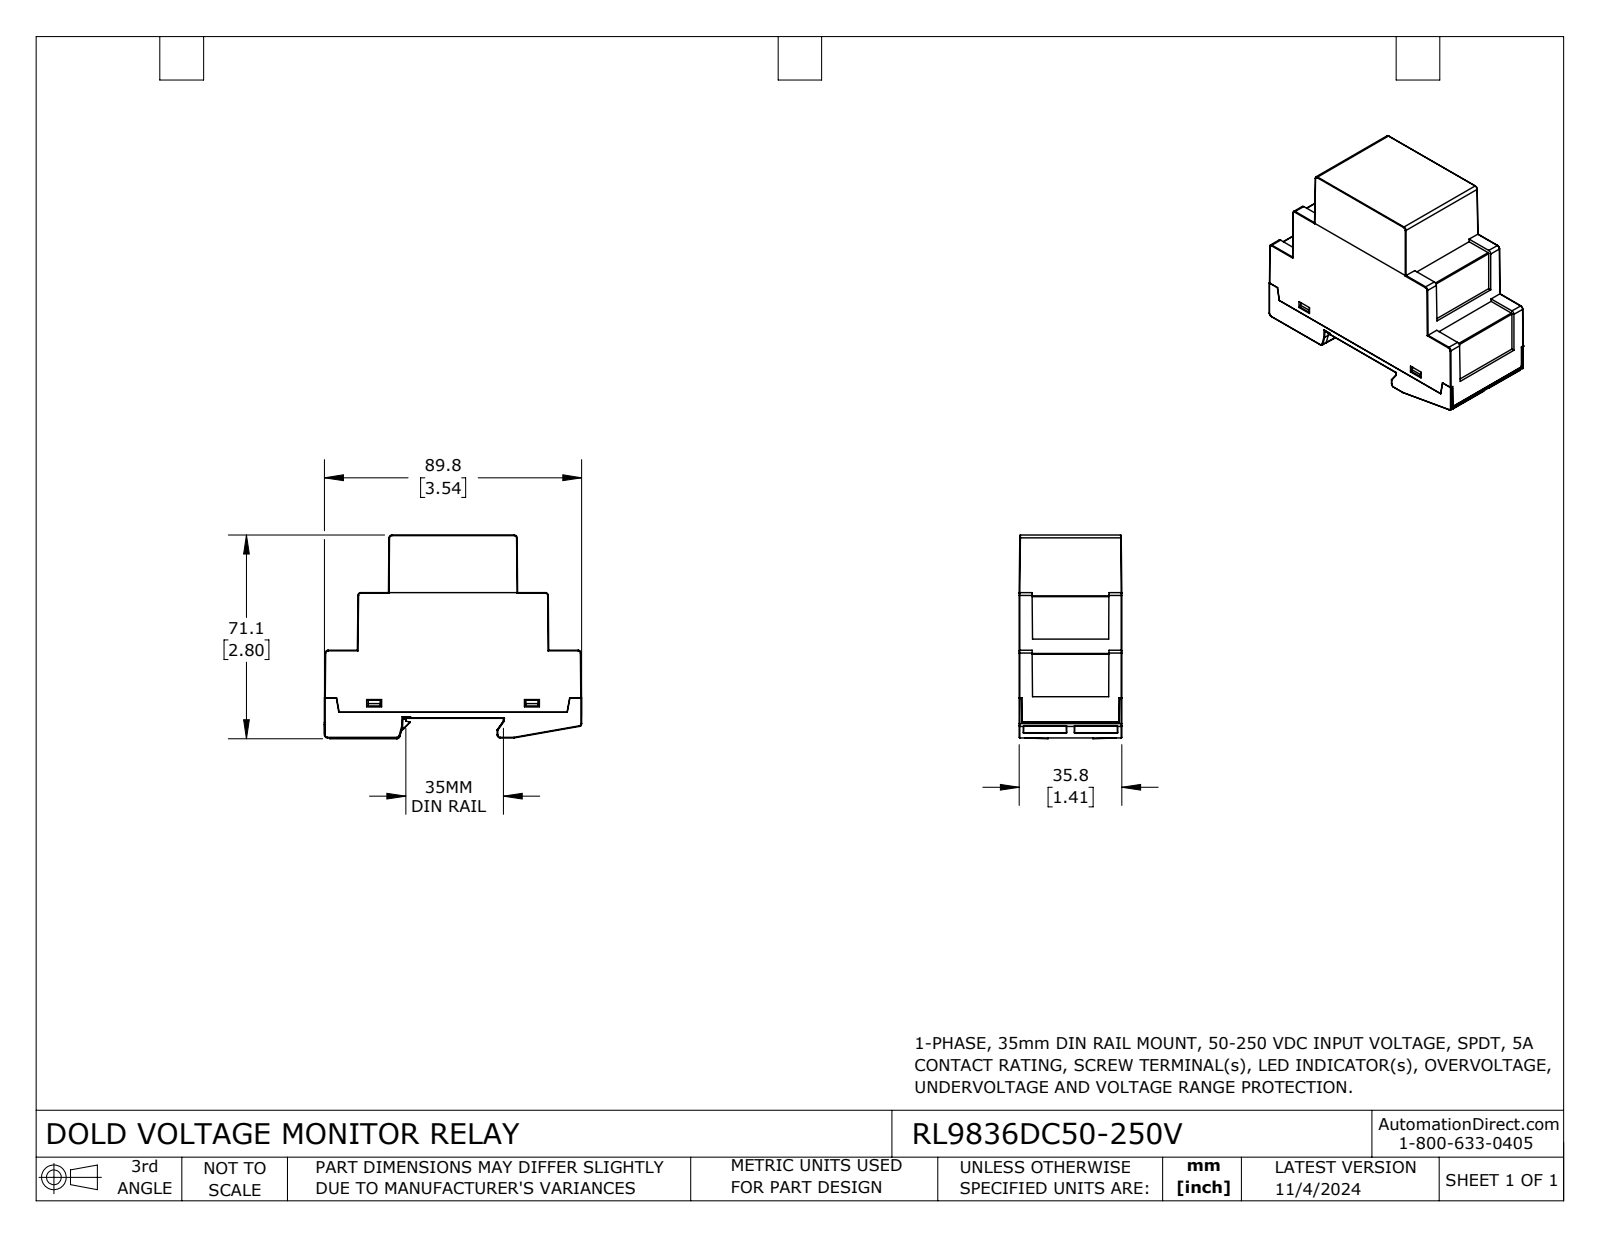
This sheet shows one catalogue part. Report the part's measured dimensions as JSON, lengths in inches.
{"part_name": "RL9836DC50-250V", "step_written_by": "SolidWorks 2023 (CONFIG_CONTROL_DESIGN)", "units": "inches", "bodies": {"solids": 2, "faces": 631, "planar": 484, "cylindrical": 109, "other": 38}, "overall_size": [3.538, 2.799, 1.409], "volume_in3": 9.341, "surface_area_in2": 55.26, "round_bosses_or_shafts": [[0.098, 2], [0.315, 1]], "partial_cylinders_radius": [[0.008, 42], [0.039, 14], [0.02, 11], [0.004, 6], [0.012, 4], [0.011, 1], [0.016, 1], [0.028, 1]], "face_to_face_distances": [1.409, 0.217, 2.52, 0.035, 0.085, 2.435, 2.219, 0.301, 0.824, 1.374]}
